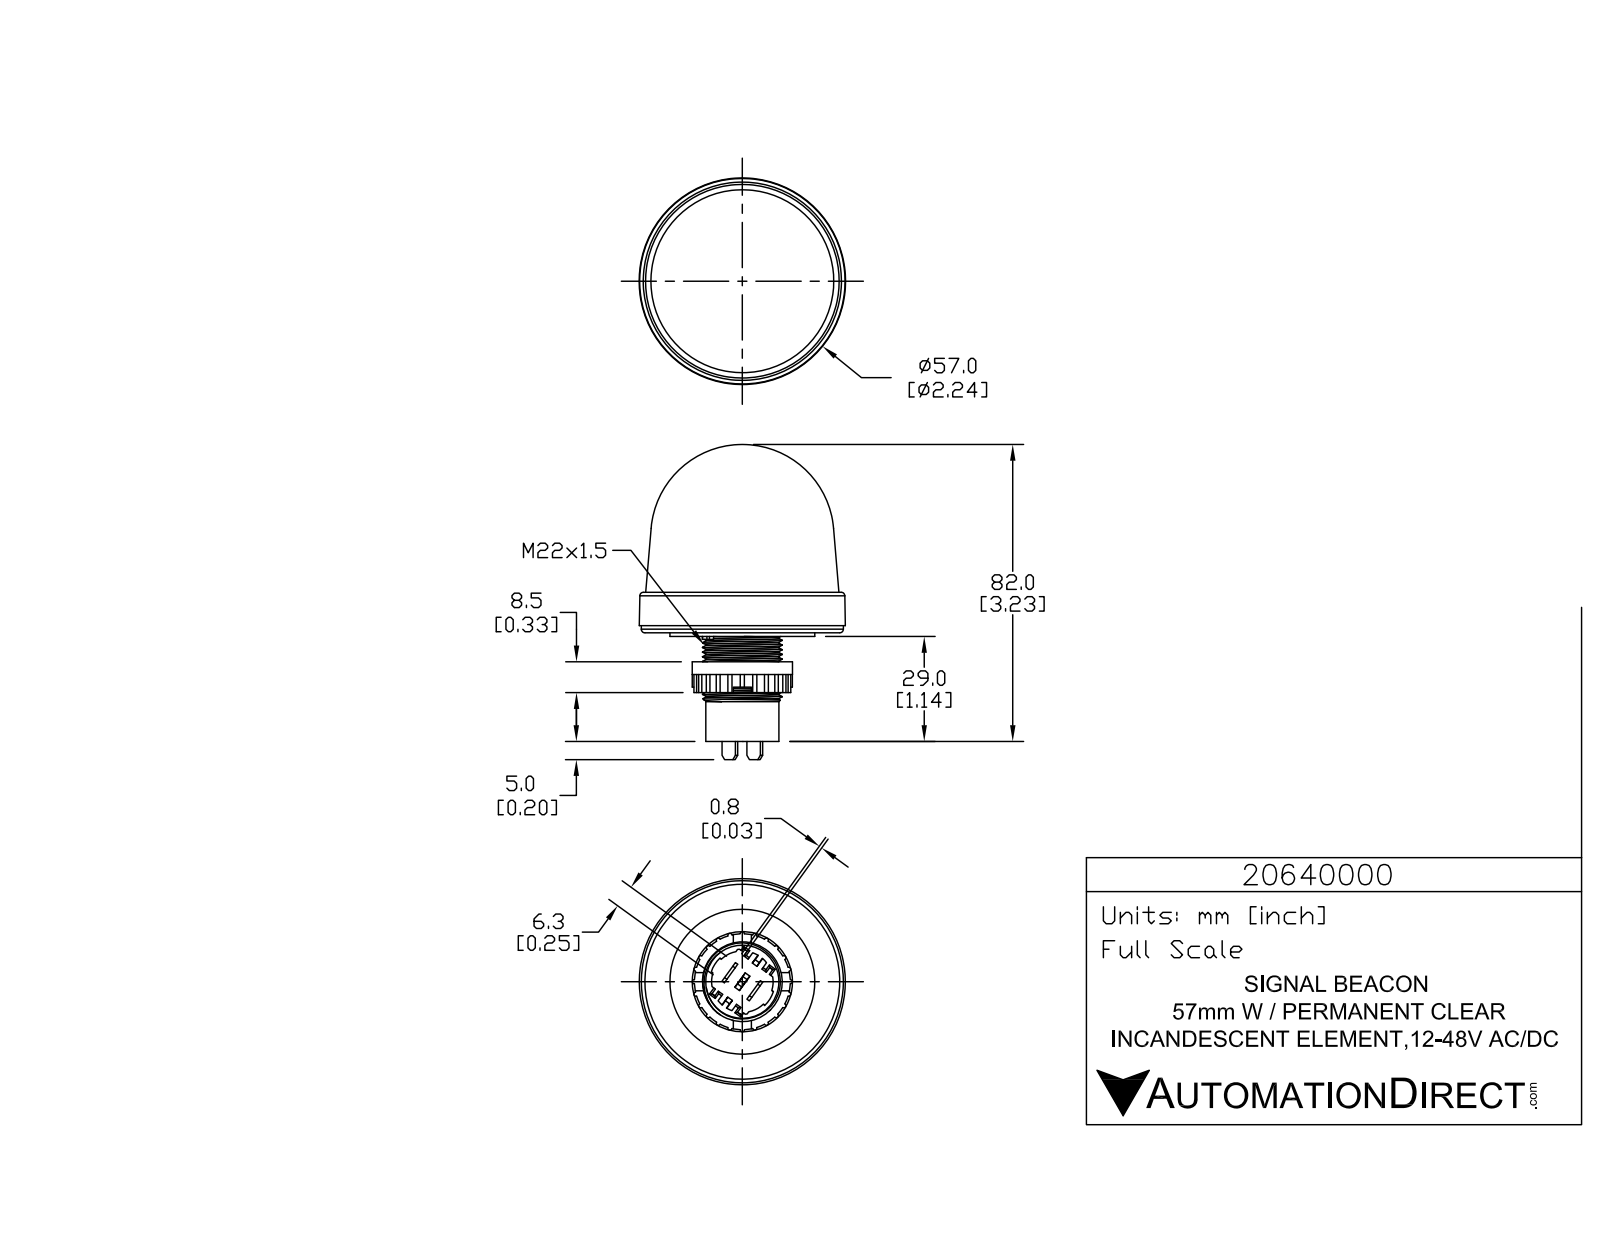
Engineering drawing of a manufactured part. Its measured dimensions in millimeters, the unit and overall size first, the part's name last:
Units: millimetres
Overall size (bounding box): 86.7 × 56.9 × 56.9
Round holes (diameter × count): ⌀1 ×3, ⌀23 ×1
Round bosses / shafts (diameter × count): ⌀5.7 ×3, ⌀1.4 ×3, ⌀55.8 ×1, ⌀40 ×1, ⌀27.7 ×1, ⌀22 ×1, ⌀20.2 ×1
Partial cylindrical surfaces — rounded edges, fillets, slot ends (radius × count): R0.6 ×24, R0.2 ×6, R0.2 ×6, R0.2 ×6, R3.3 ×6, R0.1 ×3, R0.1 ×3, R0.2 ×3
Main face-to-face distances: 1, 7, 8.5, 8, 27, 19, 26, 3, 29, 10.5
Volume: 106 200 mm³ · Surface area: 16 820 mm²
Bodies: 1 solid, 1002 faces (637 planar, 266 cylindrical, 99 other)
Part name (STEP PRODUCT): 20640000
STEP written by: SolidWorks 2015 (AUTOMOTIVE_DESIGN)
